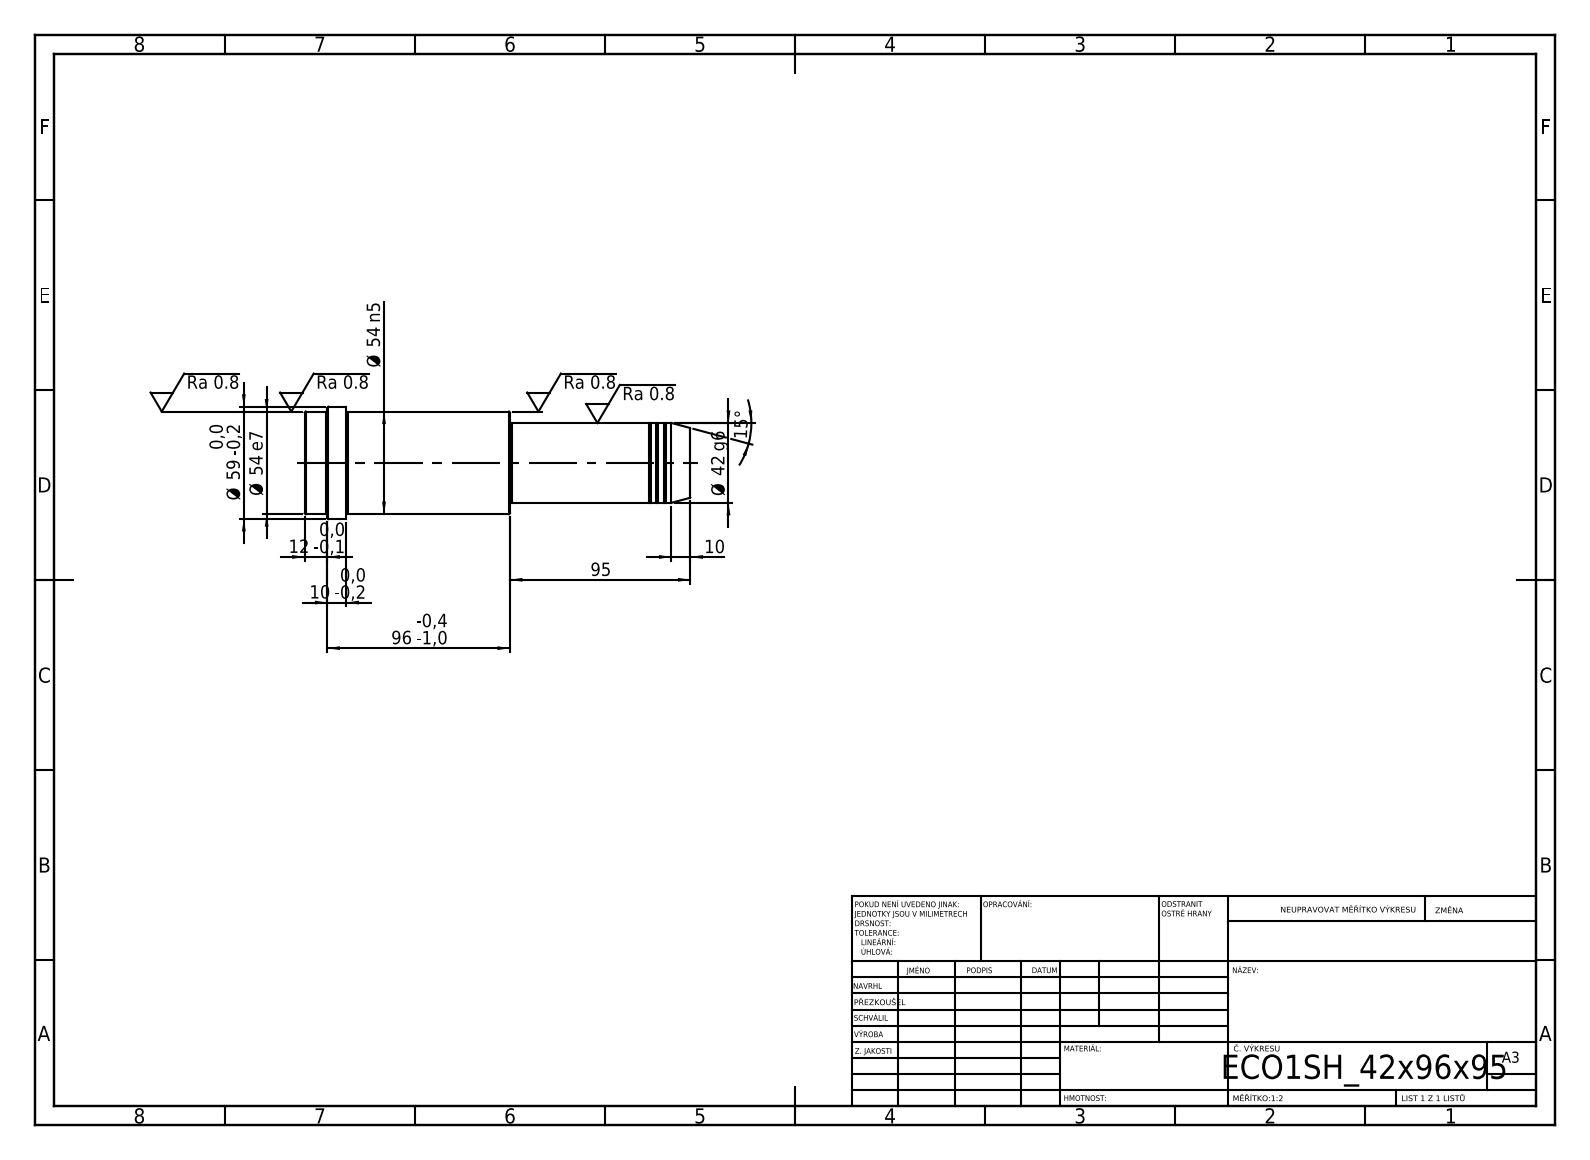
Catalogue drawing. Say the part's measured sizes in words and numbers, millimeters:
Its 3-D file was written by "SolidWorks 2019 (CONFIG_CONTROL_DESIGN)". It is 1 solid with 52 faces: 6 planar, 16 cylindrical and 30 other. Overall it measures 203 by 59 by 59 millimeters. Its volume is 381 286 cubic millimeters and its surface area 36 474 square millimeters. Round bosses or shafts: 1 of diameter 59, 1 of diameter 54, 1 of diameter 42, 1 of diameter 41. The main face-to-face distances are 203, 95, 108, 181, 86, 22, 191, 96, 10, 12.
